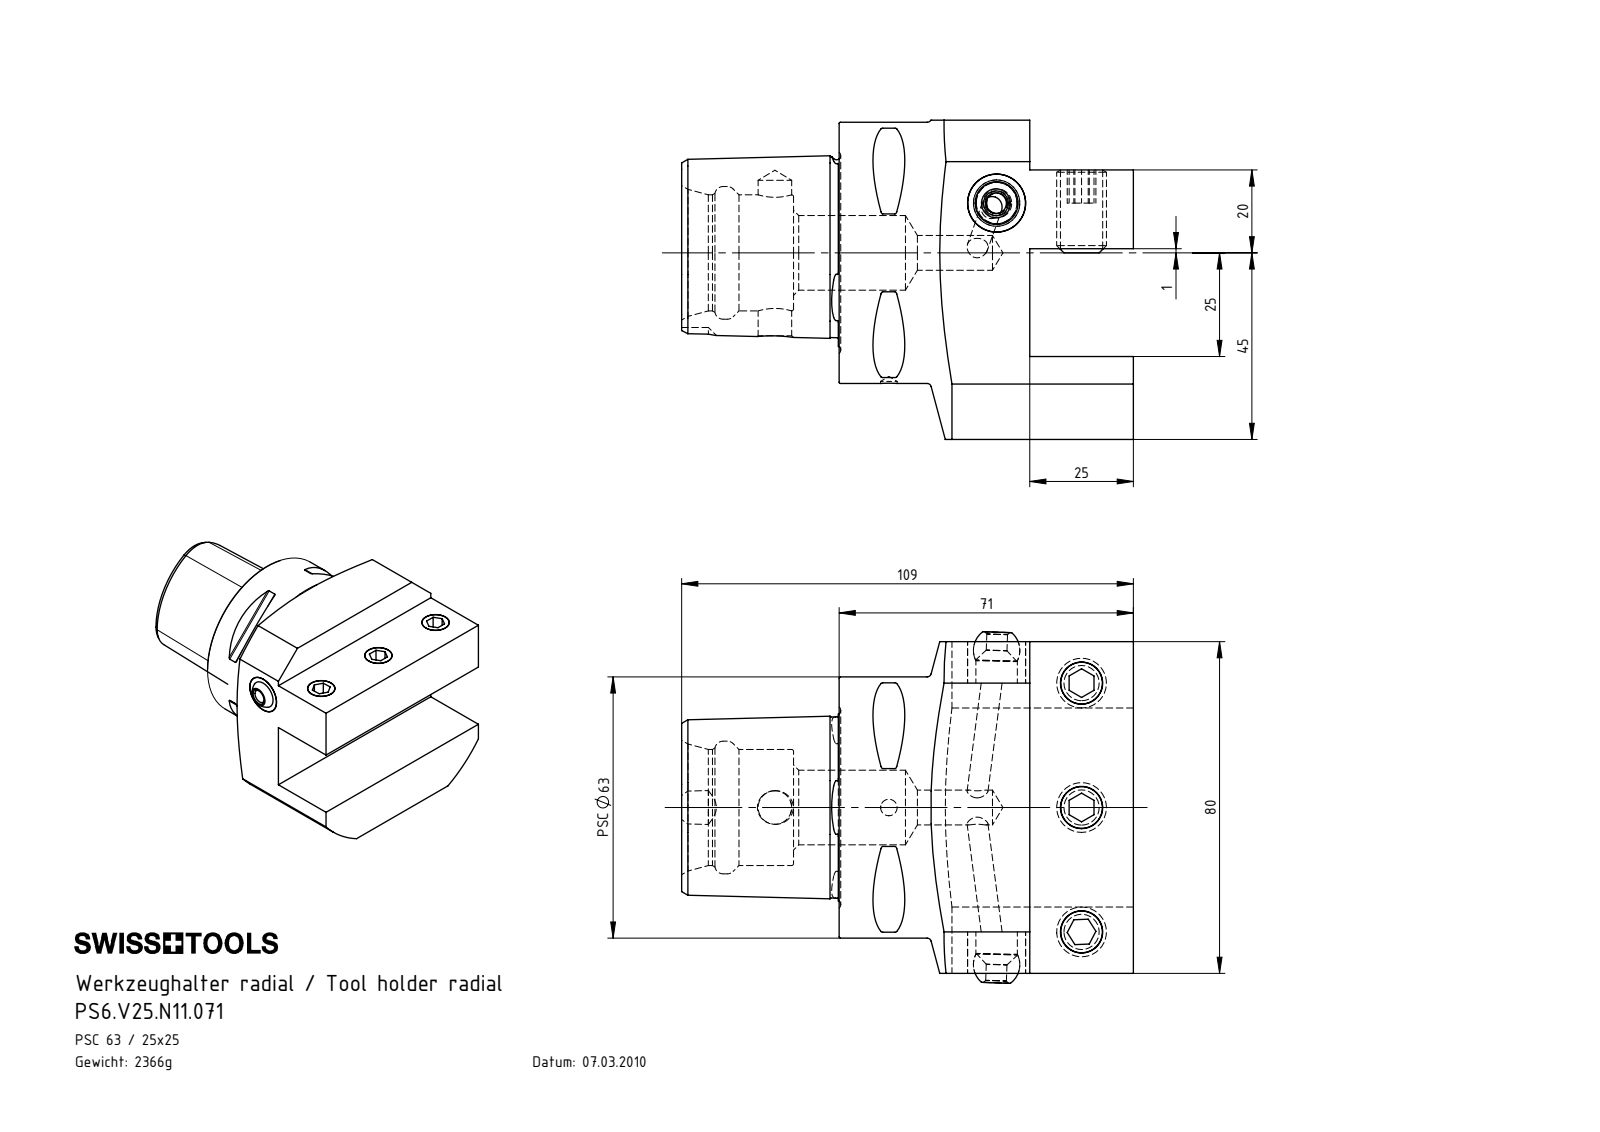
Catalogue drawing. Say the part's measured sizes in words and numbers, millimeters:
The part is named "PS6.V25.N11.071; KU1-U14.001.012_1; ISO 4026 - M12 x 20; KU1-U14.001.012_2 (+2 more)". Its 3-D file was written by "SolidWorks 2017 (AUTOMOTIVE_DESIGN)". It is 8 solids with 235 faces: 66 planar, 61 cylindrical and 108 other. Overall it measures 109 by 85.63 by 77 millimeters. Its volume is 302 548 cubic millimeters and its surface area 50 469 square millimeters. Round holes: 4 of diameter 5, 3 of diameter 10.2, 1 of diameter 4, 1 of diameter 8.1, 1 of diameter 8.4, 1 of diameter 10, 1 of diameter 14, 1 of diameter 18, 1 of diameter 28, 1 of diameter 32. Round bosses or shafts: 3 of diameter 12, 1 of diameter 63. Partial cylindrical surfaces (rounded edges, fillets, slot ends): 8 of radius 0.5, 1 of radius 6, 1 of radius 51. The main face-to-face distances are 25, 46, 20, 45, 65, 26, 19, 57, 80, 12. The hole center spacings are 30, 55.34, 79.85, 27.5, 46.5, 60, 74.
